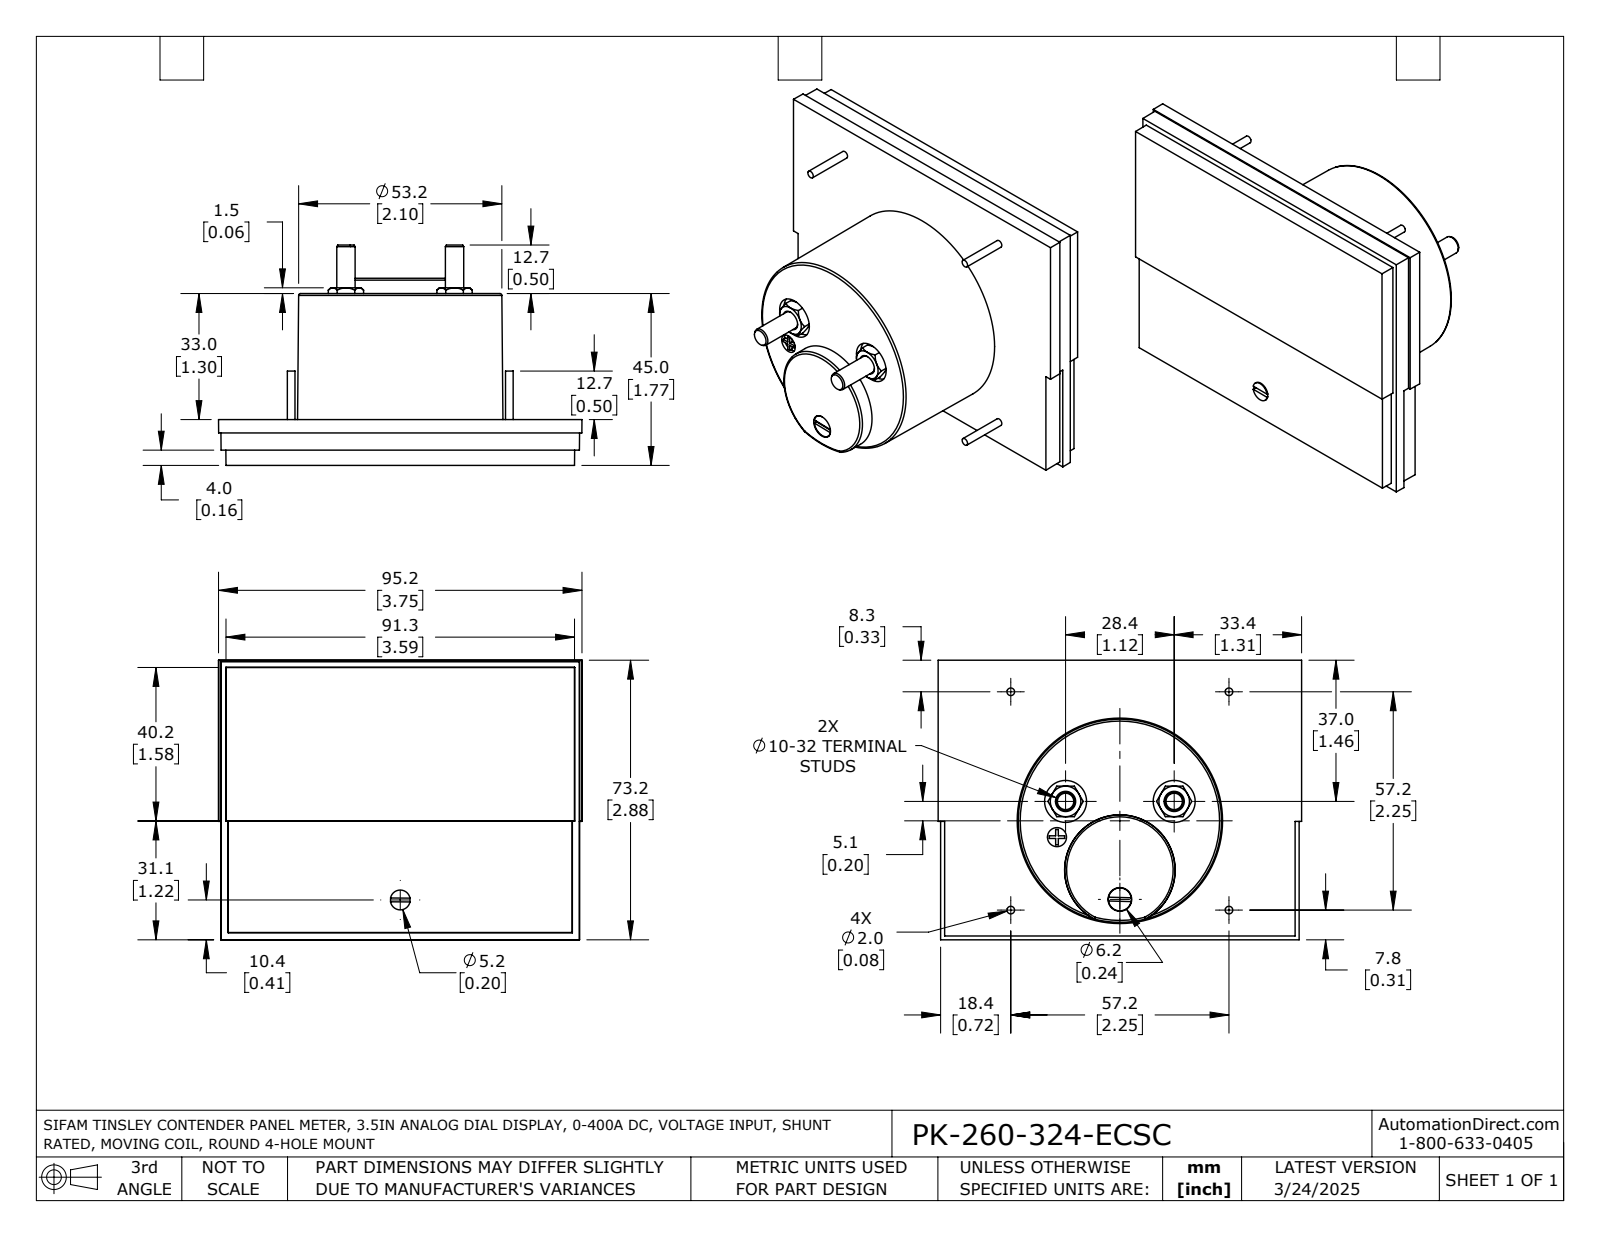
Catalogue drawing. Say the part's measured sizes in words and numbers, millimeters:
The part is named "PK-260-324-ECSC". Its 3-D file was written by "SolidWorks 2021 (AUTOMOTIVE_DESIGN)". It is 1 solid with 163 faces: 76 planar, 31 cylindrical and 56 other. Overall it measures 95.2 by 73.2 by 57.7 millimeters. Its volume is 154 800 cubic millimeters and its surface area 24 770 square millimeters. Round holes: 2 of diameter 11, 1 of diameter 5, 1 of diameter 6.2. Round bosses or shafts: 4 of diameter 2, 2 of diameter 4.8, 1 of diameter 6, 1 of diameter 5.2. Partial cylindrical surfaces (rounded edges, fillets, slot ends): 1 of radius 2.5. The main face-to-face distances are 12, 0.8, 11.3, 45, 33, 44.2, 4, 1.9, 8, 37. The hole center spacings are 29.3, 9.6, 23.2, 28.4, 32.1.
